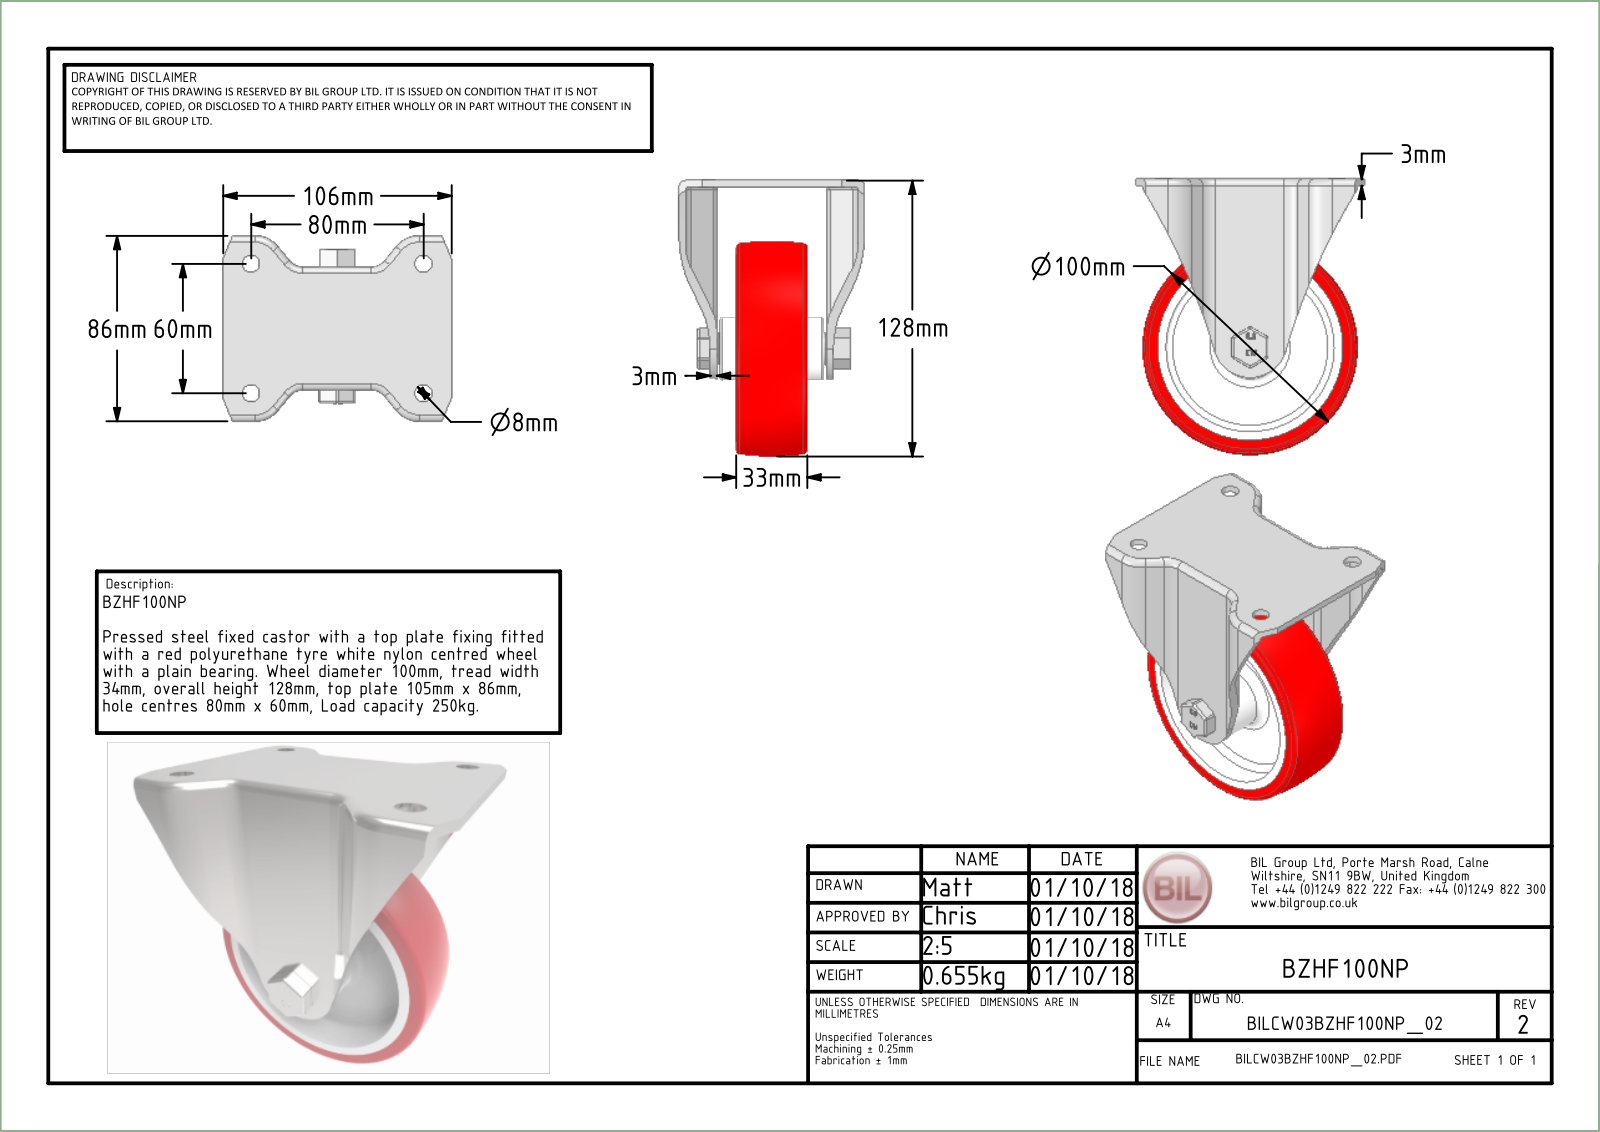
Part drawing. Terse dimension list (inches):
name: BZHF100NP v4; BZHF100AS v1; ZINC PLATED, PRESSED STEEL BRACKET; BZH100WNP61 v1 (+8 more)
written by: Autodesk Translation Framework v14.10.0.0 (AUTOMOTIVE_DESIGN)
unit: in
bodies: 7 solids, 359 faces (136 planar, 131 cylindrical, 92 other)
size: 5.039 × 4.173 × 3.465
volume: 13.9 in³; area: 156.7 in²
holes: 1× ⌀0.394, 1× ⌀0.404, 1× ⌀0.413, 1× ⌀0.472, 1× ⌀0.606, 1× ⌀3.228
bosses: 1× ⌀1.181, 1× ⌀0.63, 1× ⌀0.591, 1× ⌀0.388, 1× ⌀0.32
rounds: 18× R0.02, 12× R0.059, 10× R0.118, 8× R0.177, 6× R0.03, 4× R0.236, 4× R0.315, 4× R0.472
face distances: 0.118, 0.748, 0.551, 0.354, 0.906, 1.102, 1.654, 0.472, 2.126, 1.024
